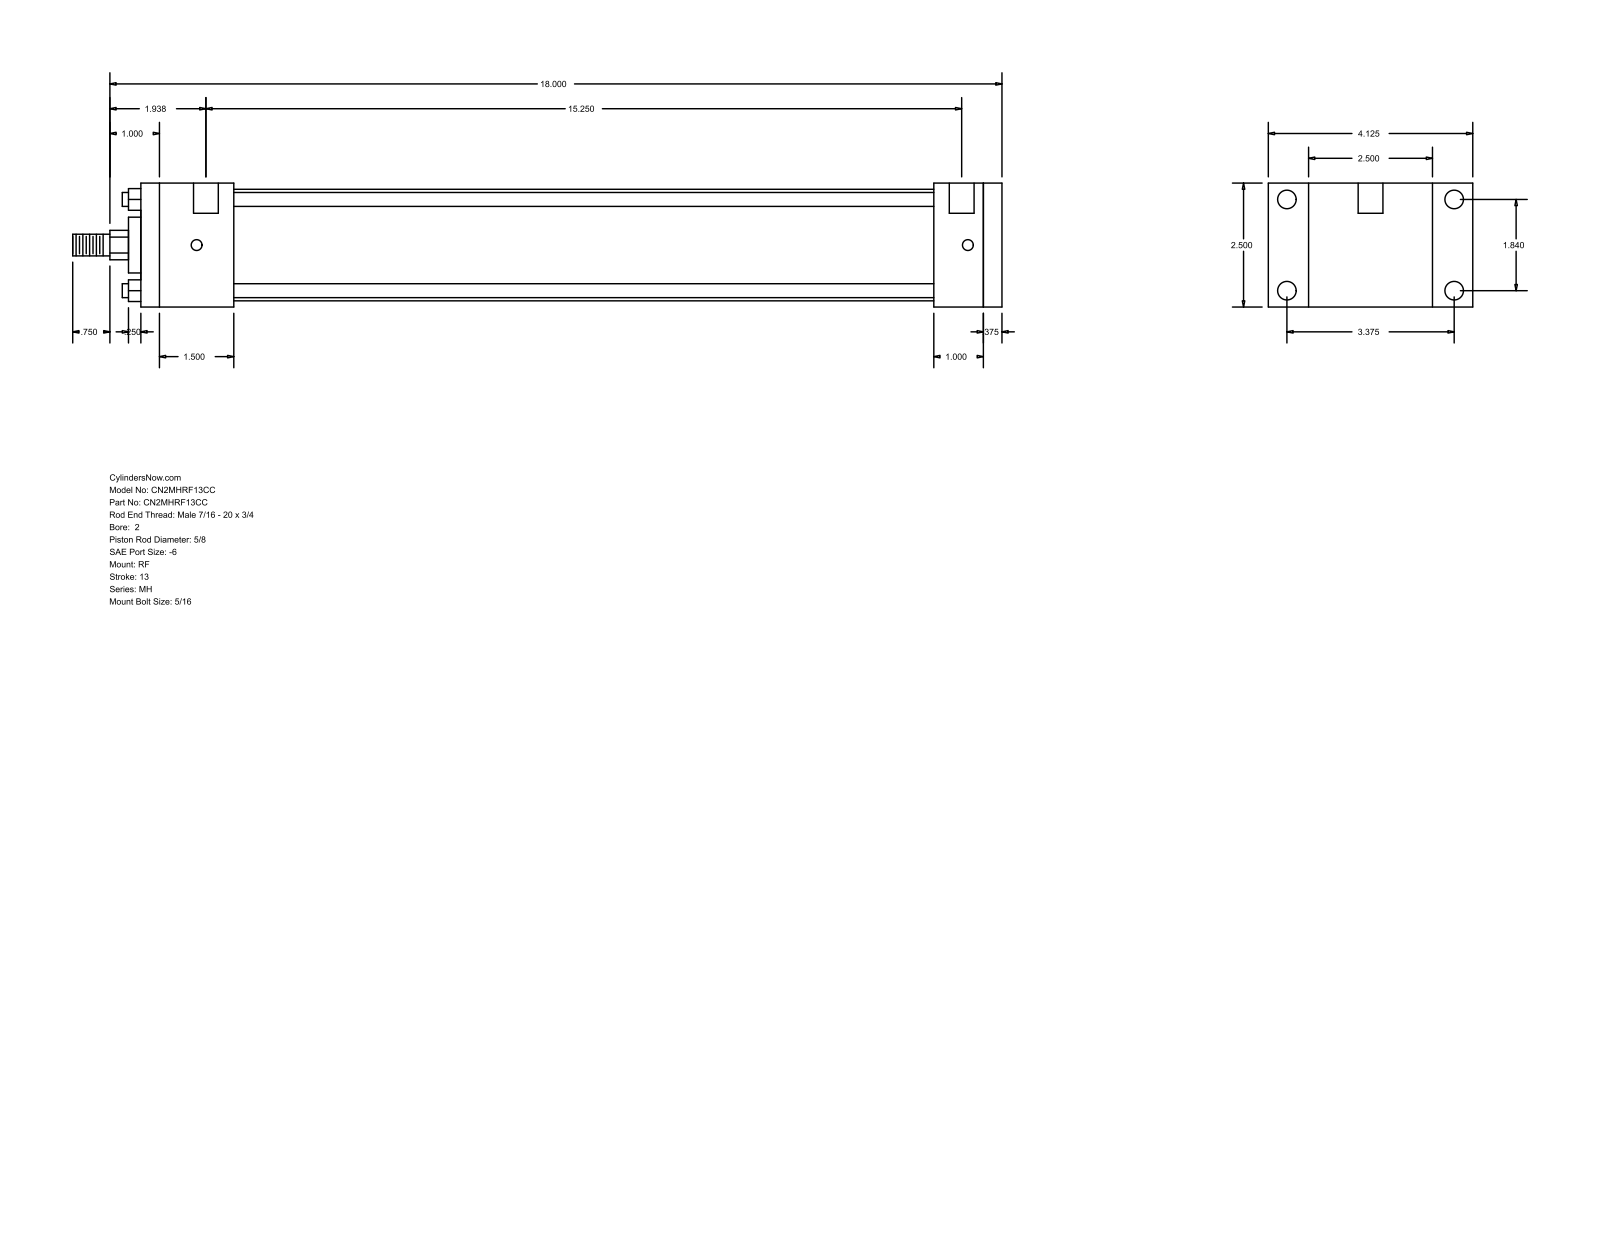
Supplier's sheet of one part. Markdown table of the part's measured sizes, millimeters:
| quantity | value |
| --- | --- |
| part name | MH_RF__0200_0.625 |
| STEP written by | GSSL Pune (CONFIG_CONTROL_DESIGN) |
| units | millimeters |
| bodies | 0 solids, 92 faces (64 planar, 28 cylindrical, 0 other) |
| overall size | 476.25 × 104.78 × 63.5 |
| round holes (diameter × count) | 5.56 × 4, 9.53 × 4, 12.7 × 2 |
| round bosses / shafts (diameter × count) | 7.14 × 4, 57.15 × 1, 28.57 × 1, 15.88 × 1, 11.11 × 1 |
| partial cylindrical surfaces (radius × count) | 7.54 × 1 |
| main face-to-face distances | 63.5, 441.32, 431.8, 9.52, 34.93, 47.62, 406.39, 358.77, 384.18, 393.7 |
| hole center spacings | 46.74, 85.72, 97.63, 395.29, 3.18, 4.76, 387.35, 390.53 |
